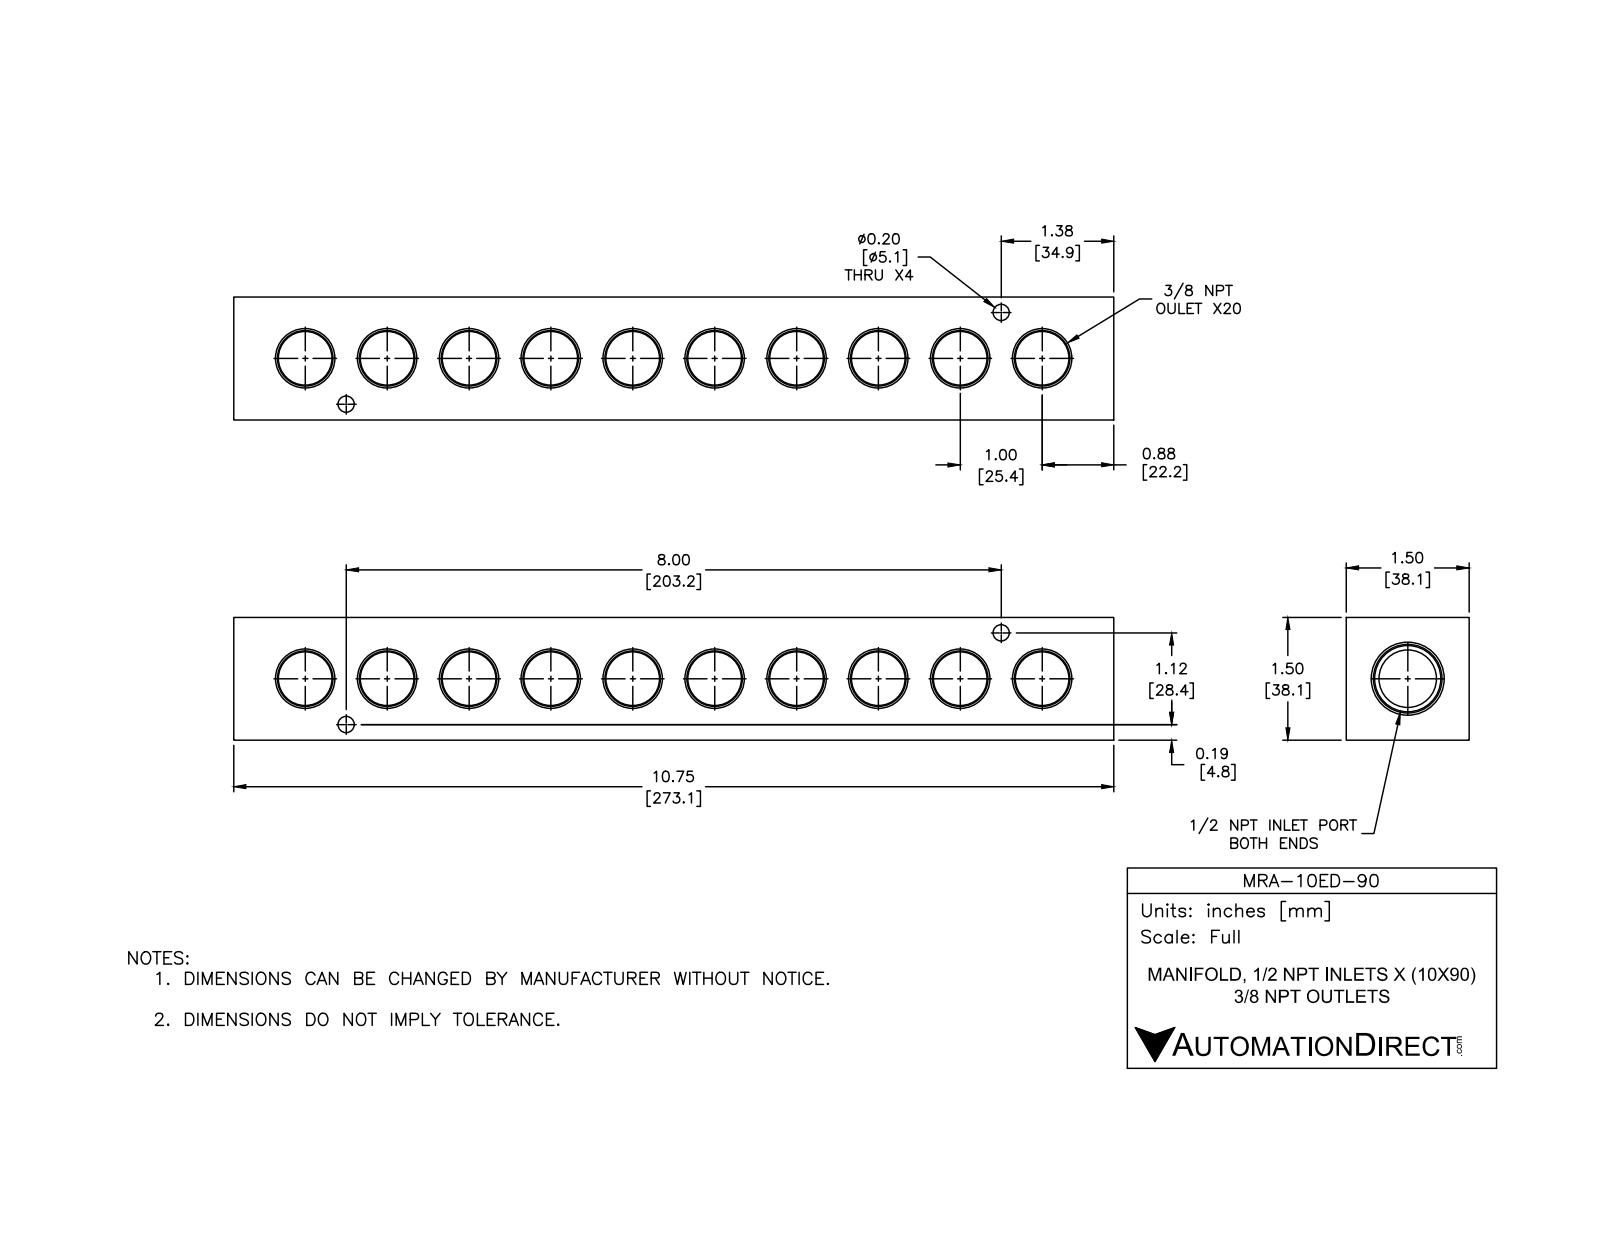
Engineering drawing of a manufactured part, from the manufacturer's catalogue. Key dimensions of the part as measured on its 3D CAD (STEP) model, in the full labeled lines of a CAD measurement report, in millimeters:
Part name (STEP PRODUCT): MRA-10ED-90
STEP written by: SolidWorks 2015 (CONFIG_CONTROL_DESIGN)
Units: millimetres
Bodies: 1 solid, 194 faces (48 planar, 58 cylindrical, 88 other)
Overall size (bounding box): 273.1 × 38.1 × 38.1
Volume: 274 200 mm³ · Surface area: 65 940 mm²
Round holes (diameter × count): ⌀14.3 ×20, ⌀5.1 ×4, ⌀17.9 ×1
Main face-to-face distances: 38.1, 273.1, 27.7, 10.4, 13.5, 259.6, 246.1
Hole centre spacings: 25.4, 50.8, 76.2, 101.6, 127, 19.1, 152.4, 177.8
